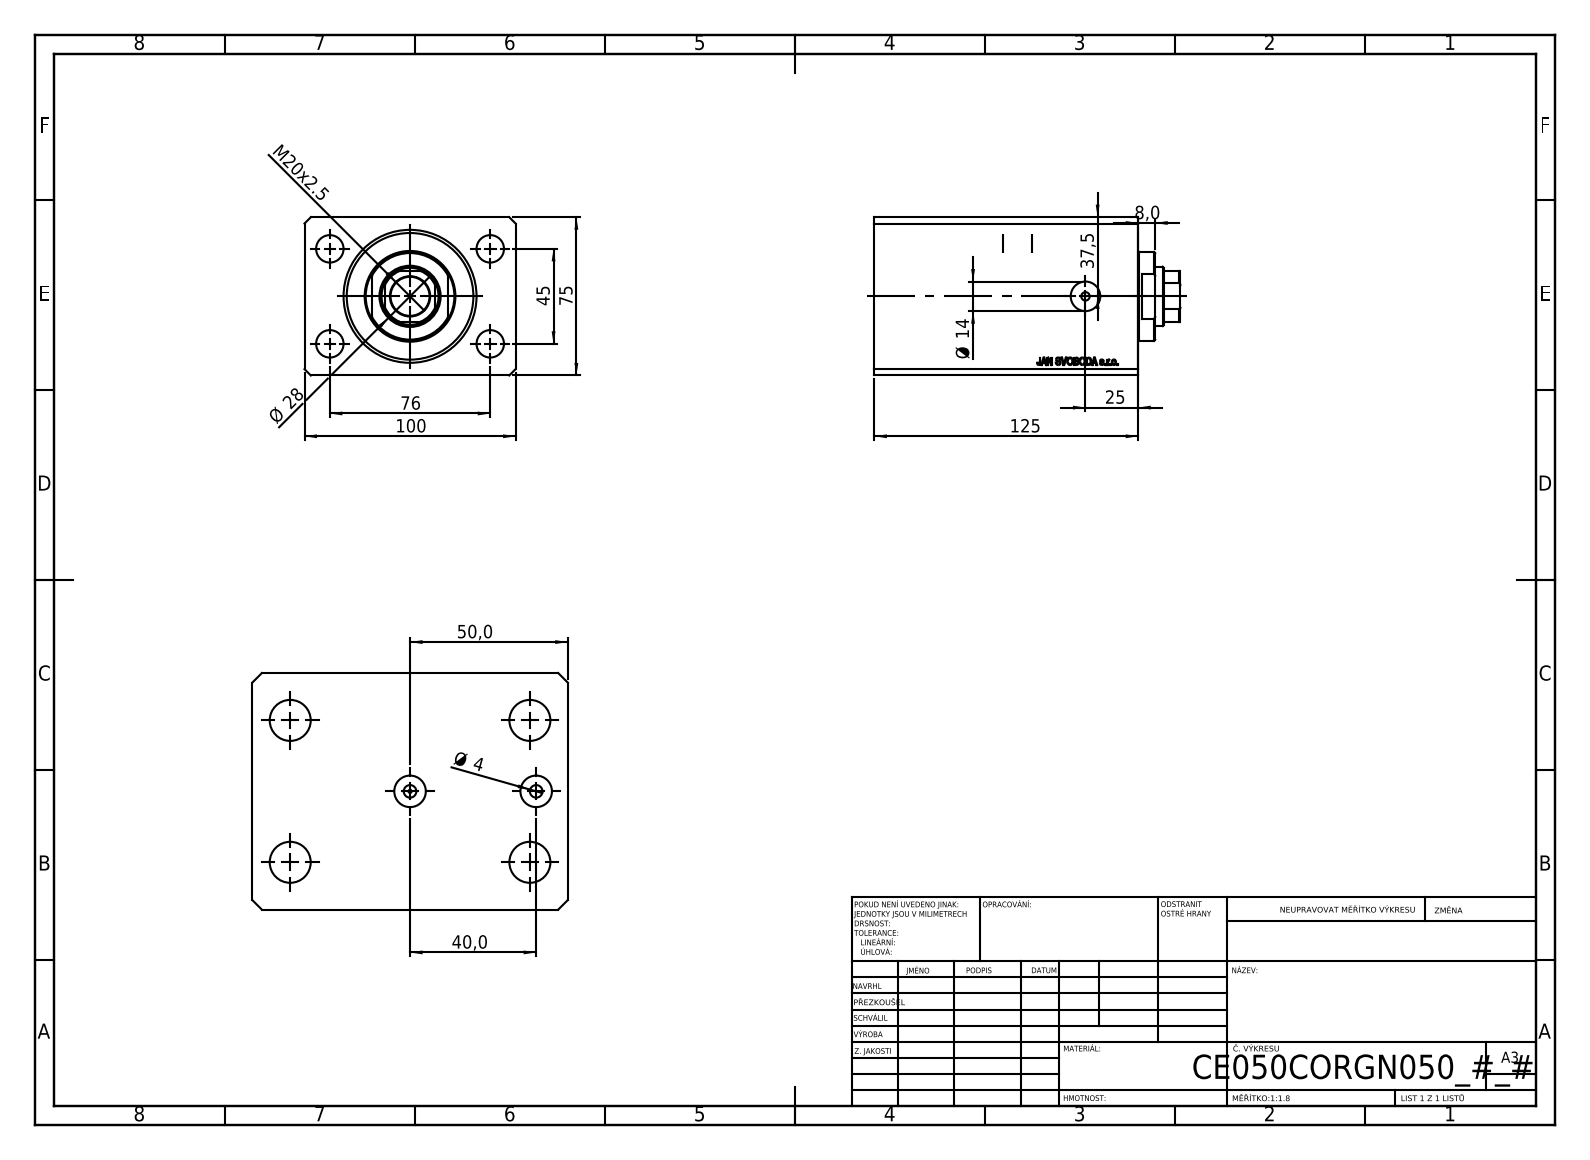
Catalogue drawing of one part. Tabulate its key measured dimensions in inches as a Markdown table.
| quantity | value |
| --- | --- |
| part name | V250CE_VC_C; V250CE_C_VCP; V250CE_C_Body |
| STEP written by | SolidWorks 2019 (CONFIG_CONTROL_DESIGN) |
| units | inches |
| bodies | 3 solids, 868 faces (428 planar, 46 cylindrical, 394 other) |
| overall size | 5.709 × 3.937 × 2.953 |
| volume | 49.15 in³ |
| surface area | 203.5 in² |
| round holes (diameter × count) | 0.157 × 4, 0.512 × 4, 0.394 × 2, 0.551 × 2, 0.049 × 1, 0.728 × 1, 1.102 × 1, 1.969 × 1, 2.48 × 1 |
| round bosses / shafts (diameter × count) | 1.654 × 1 |
| partial cylindrical surfaces (radius × count) | 0.531 × 1 |
| main face-to-face distances | 2.953, 3.937, 4.921, 0.469, 4.453, 0.787, 4.134, 3.665, 2.756, 2.165 |
| hole center spacings | 1.739, 0.889, 1.772, 2.992, 3.196, 3.477, 1.575, 2.953 |
